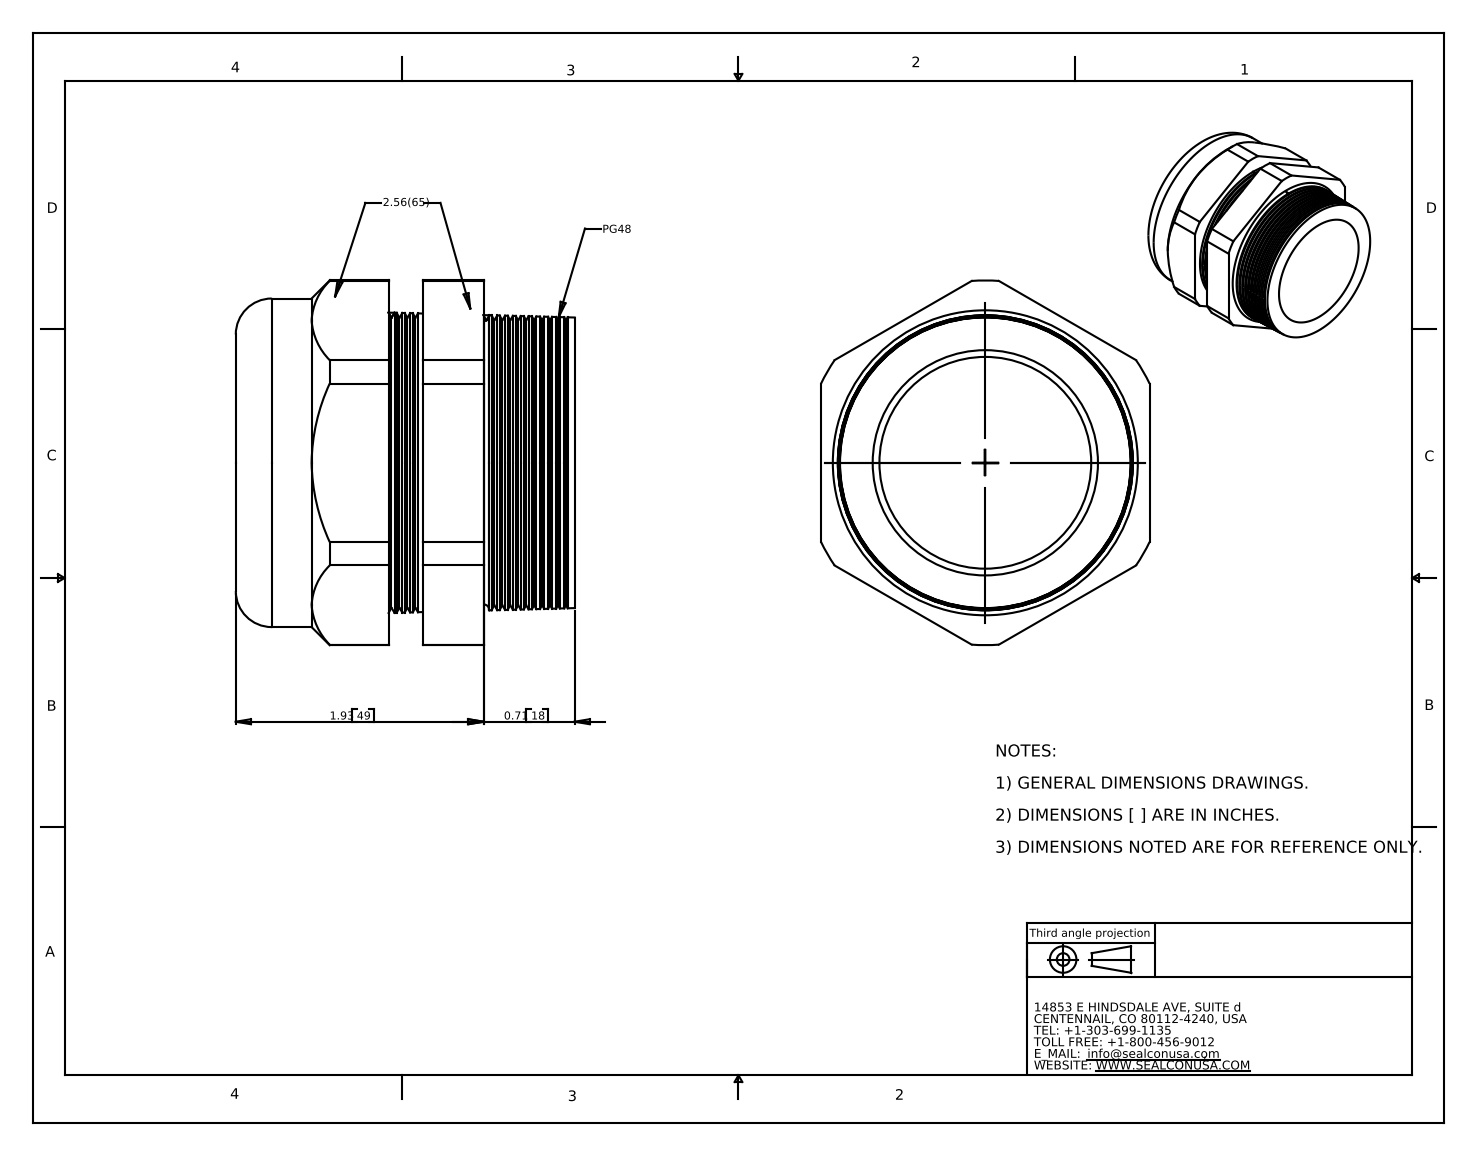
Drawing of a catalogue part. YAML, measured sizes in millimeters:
part_name: "CD48CA-BK"
step_written_by: "SolidWorks 2007 (CONFIG_CONTROL_DESIGN)"
units: millimeters
bodies: {solids: 2, faces: 146, planar: 20, cylindrical: 22, other: 104}
overall_size: [72.2, 67.1, 65]
volume: 115200
surface_area: 35050
round_holes:
  - {diameter: 41.9, count: 1}
  - {diameter: 44.6, count: 1}
round_bosses_or_shafts:
  - {diameter: 65, count: 1}
partial_cylinders:
  - {radius: 36.1, count: 1}
face_to_face_distances: [65, 30, 6.8, 36.8, 18.8, 12, 18, 30.3, 37, 49]
